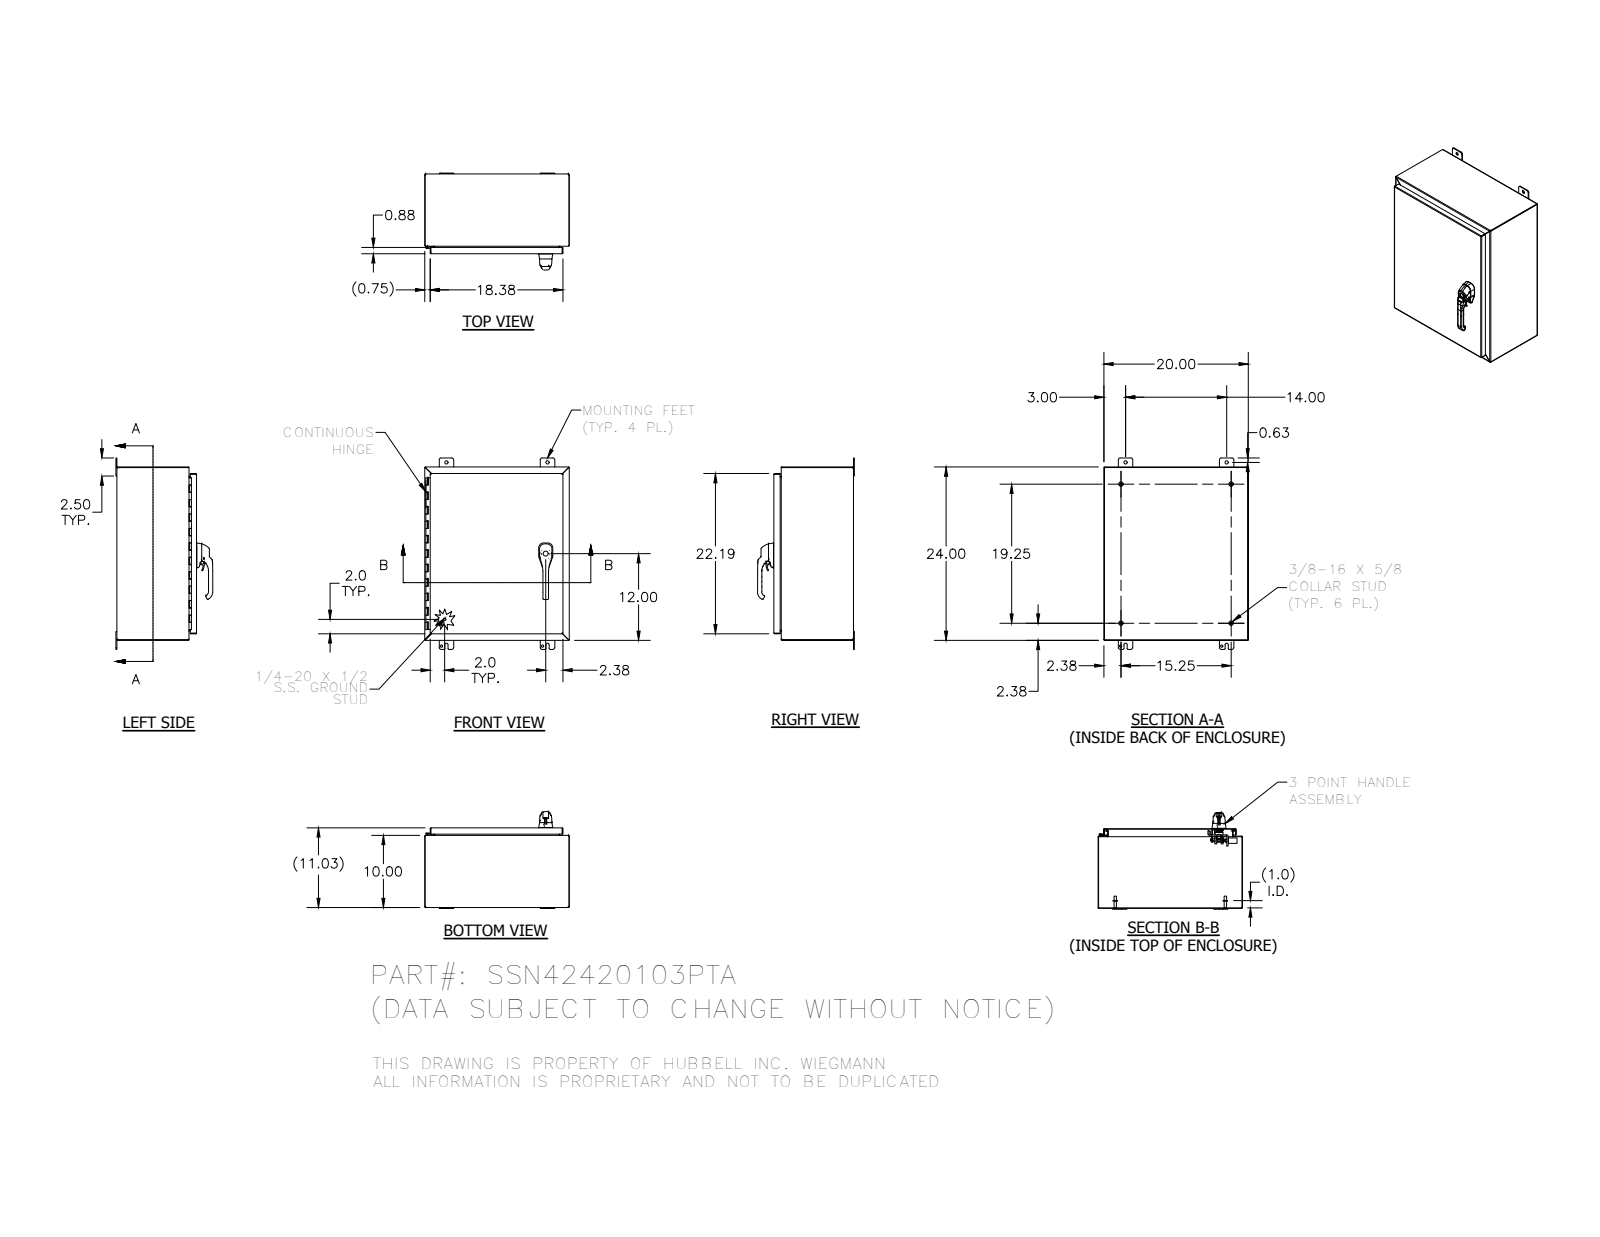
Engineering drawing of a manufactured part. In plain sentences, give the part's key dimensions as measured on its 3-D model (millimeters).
The part is named "328138L; 7379-M6-8X25_AF0; DIN985_M10; 38846 (+8 more)". Its 3-D file was written by "SolidWorks 2014 (AUTOMOTIVE_DESIGN)". It is 56 solids with 3071 faces: 1014 planar, 1270 cylindrical and 787 other. Overall it measures 673.1 by 508 by 340.6 millimeters. Its volume is 2 886 000 cubic millimeters and its surface area 2 919 000 square millimeters. Round holes: 8 of diameter 6.7, 4 of diameter 4.7, 4 of diameter 8, 4 of diameter 11.1, 3 of diameter 5.4, 3 of diameter 7.1, 2 of diameter 6.1, 2 of diameter 6.4, 2 of diameter 6.4, 2 of diameter 8, 2 of diameter 10.2, 2 of diameter 10.2. Round bosses or shafts: 4 of diameter 15.9, 4 of diameter 8.4, 3 of diameter 6, 2 of diameter 25.4, 2 of diameter 14.3, 2 of diameter 13.5, 2 of diameter 13.5, 2 of diameter 12.7. Partial cylindrical surfaces (rounded edges, fillets, slot ends): 172 of radius 0.5, 113 of radius 0.3, 26 of radius 3.2, 24 of radius 0.8, 21 of radius 0.5, 20 of radius 2.7, 20 of radius 6.4, 16 of radius 0.6. The main face-to-face distances are 1.9, 278.4, 506.1, 276.5, 280.2, 607.7, 508, 504.2, 252.1, 26.2. The hole center spacings are 9.7, 12.5, 19.3, 355.6, 705.7, 22.5, 366.5, 5.9.
